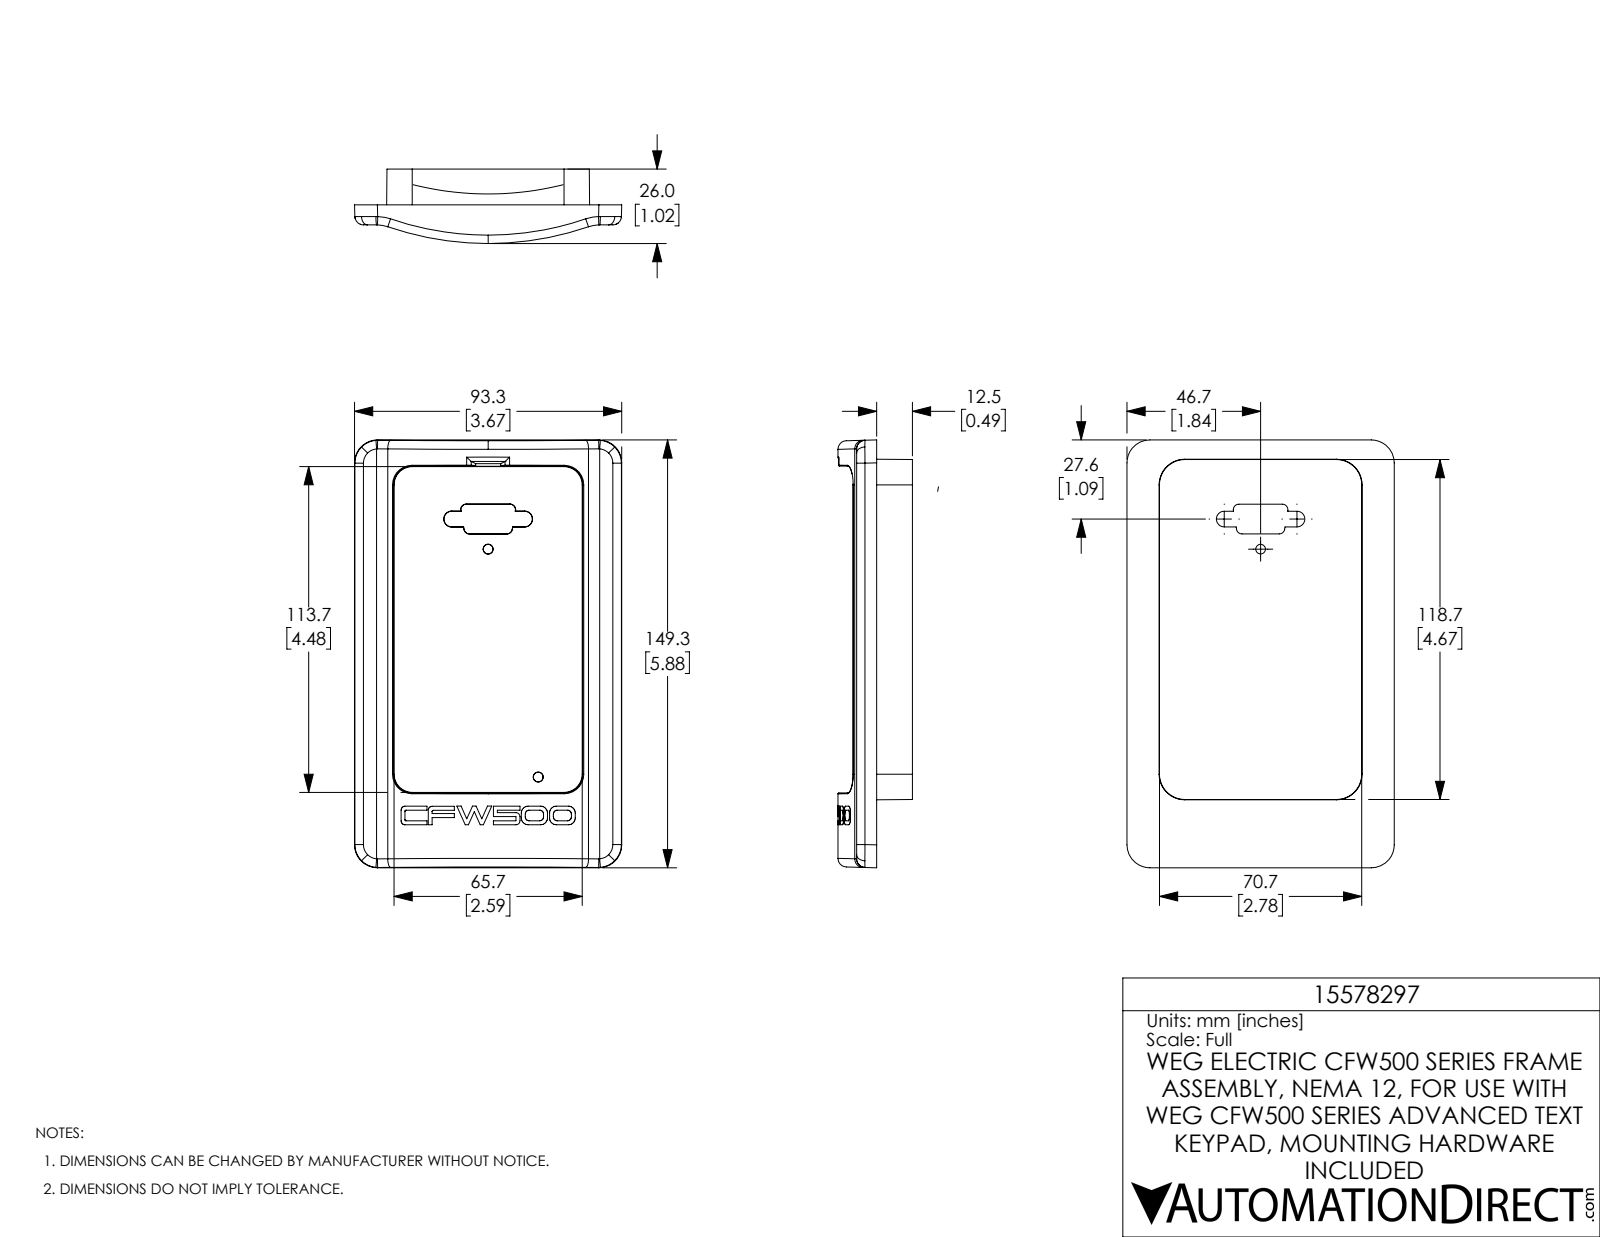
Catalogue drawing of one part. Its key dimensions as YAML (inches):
part_name: "15578297_ CONJ MOLDURA HMI CFW500_RHMIF nc"
step_written_by: "SolidWorks 2017 (AUTOMOTIVE_DESIGN)"
units: inches
bodies: {solids: 1, faces: 105, planar: 32, cylindrical: 23, other: 50}
overall_size: [5.88, 3.675, 1.024]
volume: 5.157
surface_area: 65.21
partial_cylinders:
  - {radius: 0.012, count: 4}
  - {radius: 0.315, count: 4}
  - {radius: 0.059, count: 2}
  - {radius: 0.118, count: 2}
  - {radius: 0.472, count: 2}
  - {radius: 4.252, count: 1}
face_to_face_distances: [0.098, 0.492, 0.394, 0.768, 0.669, 0.276, 5.009, 0.096, 1.304, 1.207]
